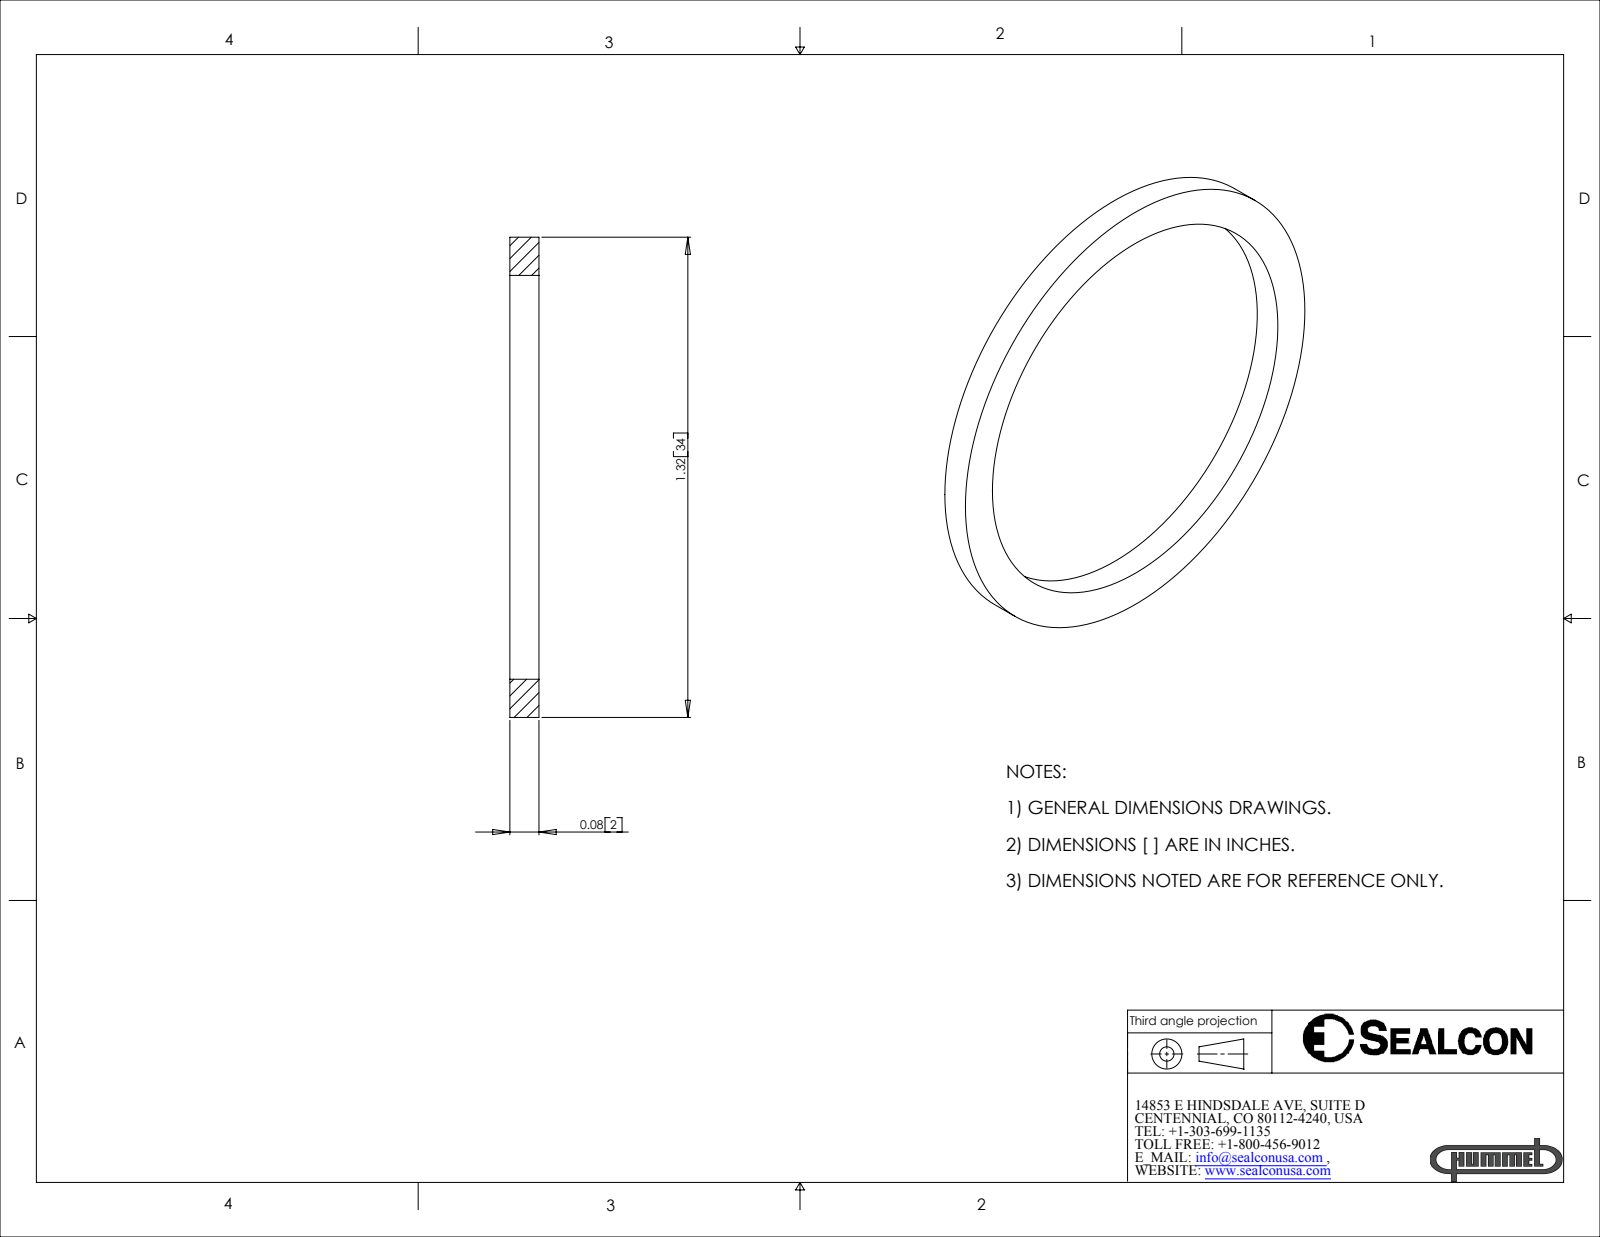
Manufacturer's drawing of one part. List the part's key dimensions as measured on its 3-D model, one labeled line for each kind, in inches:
Part name (STEP PRODUCT): SR-21-VT
STEP written by: SolidWorks 2007 (CONFIG_CONTROL_DESIGN)
Units: inches
Bodies: 1 solid, 6 faces (2 planar, 4 cylindrical, 0 other)
Overall size (bounding box): 1.32 × 1.32 × 0.08
Volume: 0.032 in³ · Surface area: 1.412 in²
Round holes (diameter × count): ⌀1.11 ×1
Round bosses / shafts (diameter × count): ⌀1.32 ×1
Main face-to-face distances: 0.08
